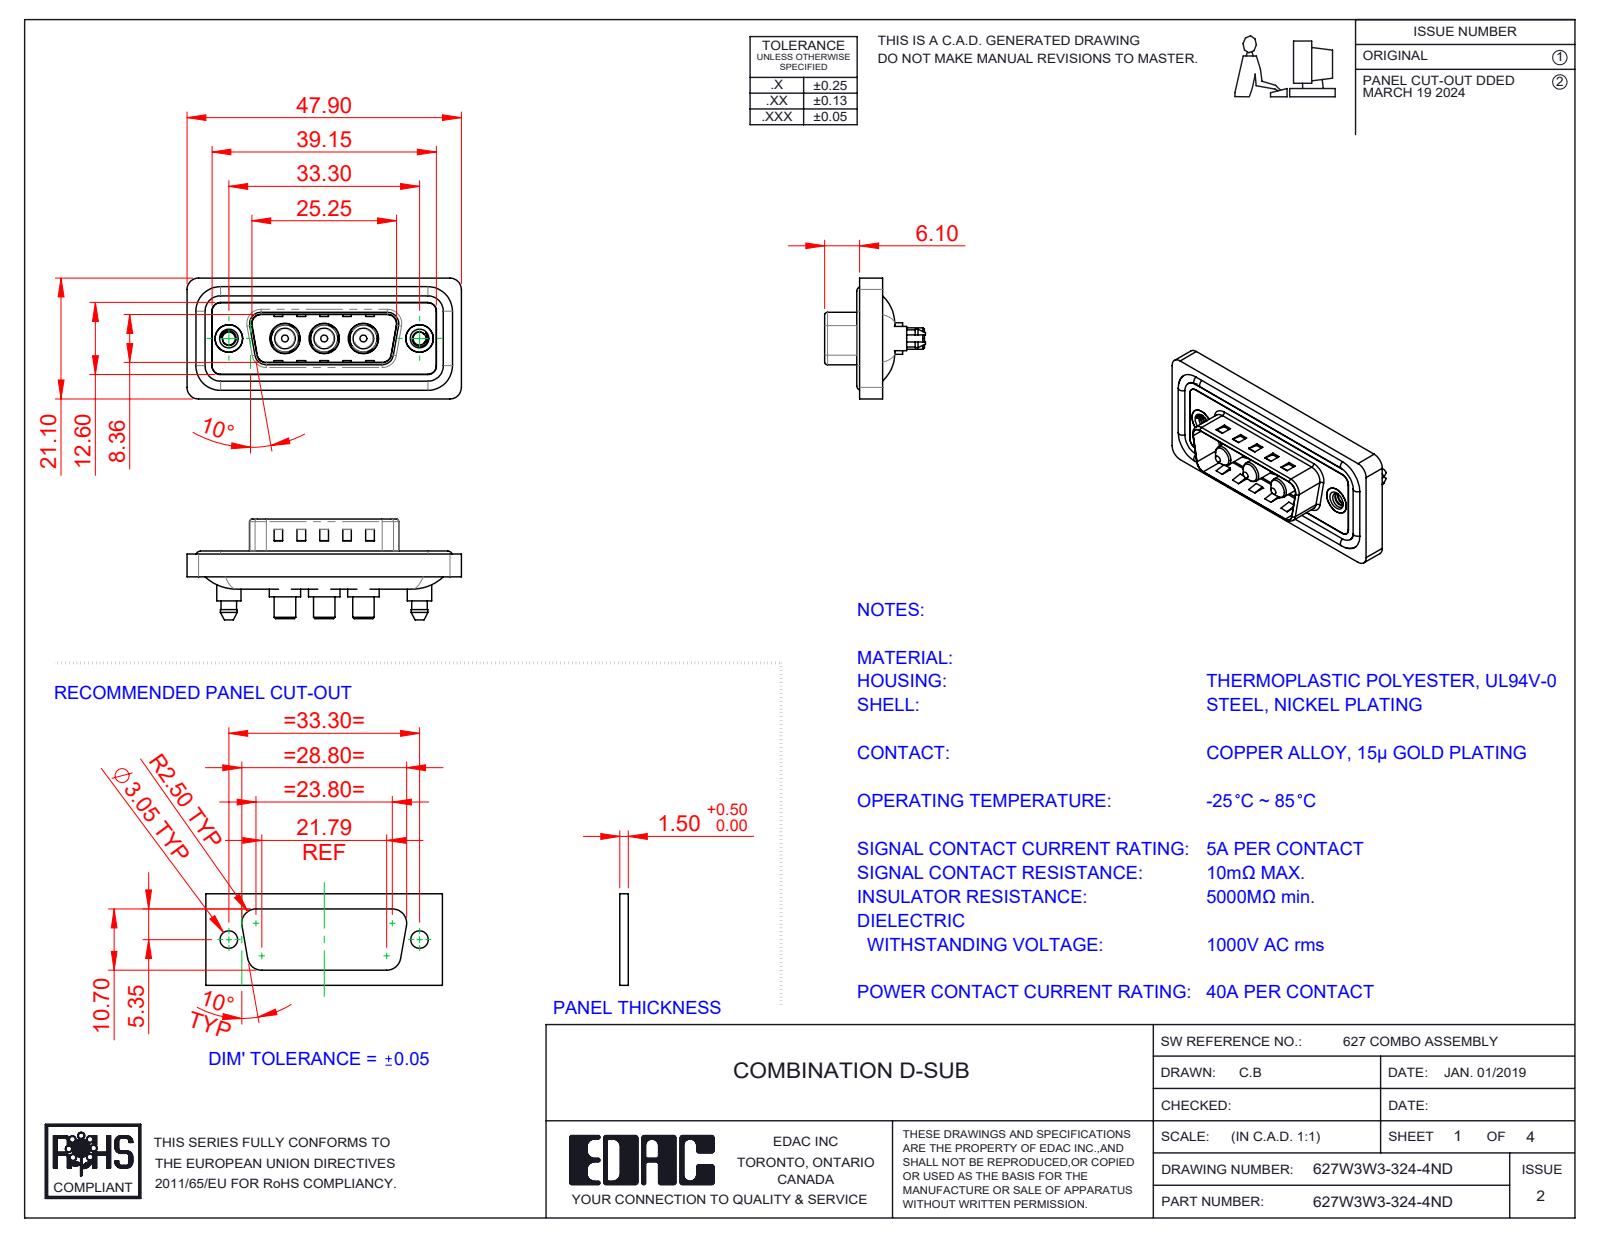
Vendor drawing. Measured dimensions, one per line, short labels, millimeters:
name: 627Combo Threaded Boardlock_D; 627Combo Waterproof Housing_15 Contacts; 627Combo Housing_3W3; Power Pin_40A S (+4 more)
written by: SolidWorks 2023 (CONFIG_CONTROL_DESIGN)
unit: mm
bodies: 13 solids, 622 faces (223 planar, 281 cylindrical, 118 other)
size: 47.9 × 21.1 × 17.6
volume: 5 776 mm³; area: 9 122 mm²
holes: 3× ⌀4.85, 3× ⌀5.3, 2× ⌀2.26, 2× ⌀4, 2× ⌀4.8, 2× ⌀5
bosses: 4× ⌀1.6, 3× ⌀5.5, 3× ⌀5.2, 3× ⌀4.75, 3× ⌀3.75, 3× ⌀3.6, 2× ⌀5.4, 2× ⌀4.9
rounds: 28× R1.5, 20× R2, 10× R1.6, 8× R0.5, 4× R0.25, 4× R0.6, 4× R0.65, 4× R0.9
face distances: 0.4, 1.1, 3.1, 1.5, 1.6, 0.5, 2.9, 4, 0.7, 0.82
hole spacings: 6.85, 9.8, 16.65, 23.5, 13.7, 33.3
